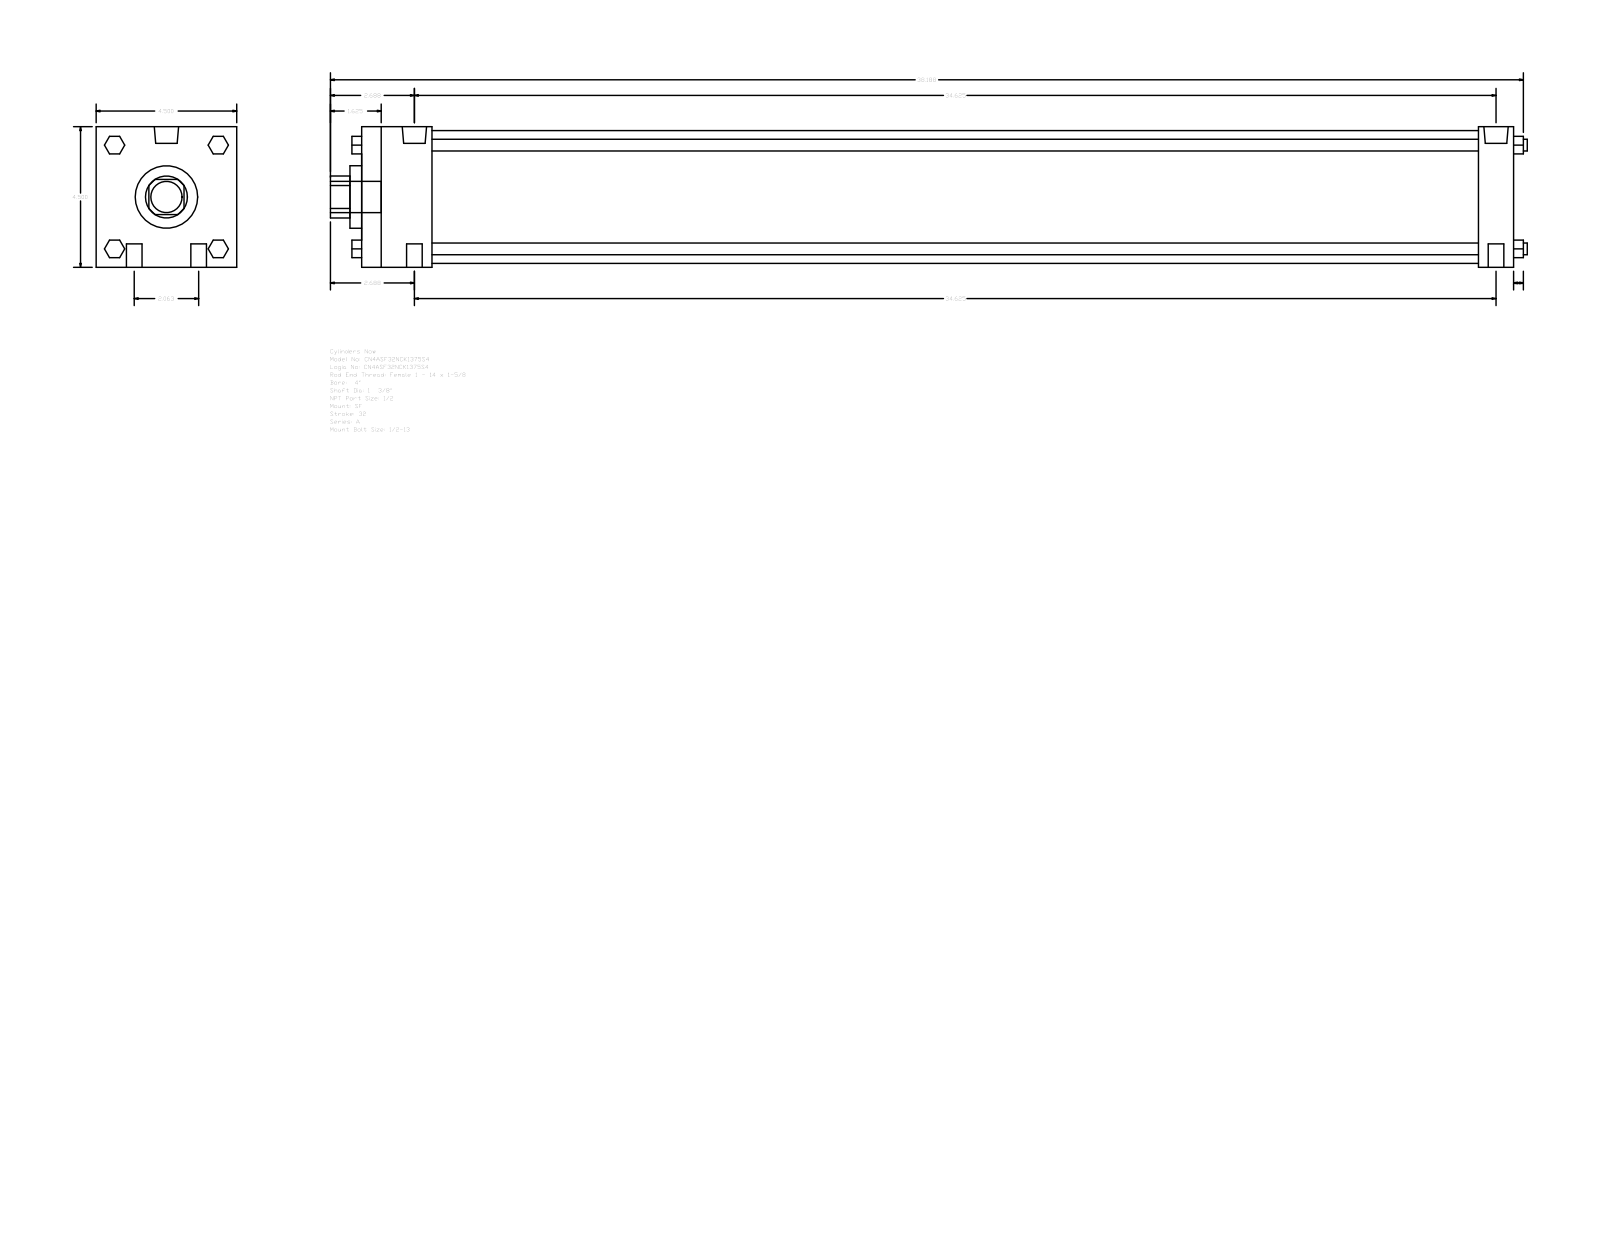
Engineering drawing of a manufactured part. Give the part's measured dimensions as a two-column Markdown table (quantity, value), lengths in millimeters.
| quantity | value |
| --- | --- |
| part name | A_SF__0400_1.375 |
| STEP written by | GSSL Pune (CONFIG_CONTROL_DESIGN) |
| units | millimeters |
| bodies | 0 solids, 124 faces (94 planar, 30 cylindrical, 0 other) |
| overall size | 973.14 × 114.3 × 114.3 |
| round holes (diameter × count) | 34.92 × 1, 50.8 × 1, 107.95 × 1 |
| round bosses / shafts (diameter × count) | 12.7 × 4, 9.53 × 4, 19.77 × 2, 8.73 × 2, 25.4 × 1 |
| partial cylindrical surfaces (radius × count) | 17.06 × 1 |
| main face-to-face distances | 114.3, 936.62, 28.57, 908.05, 57.15, 850.9, 879.47, 14.29, 9.52, 66.67 |
